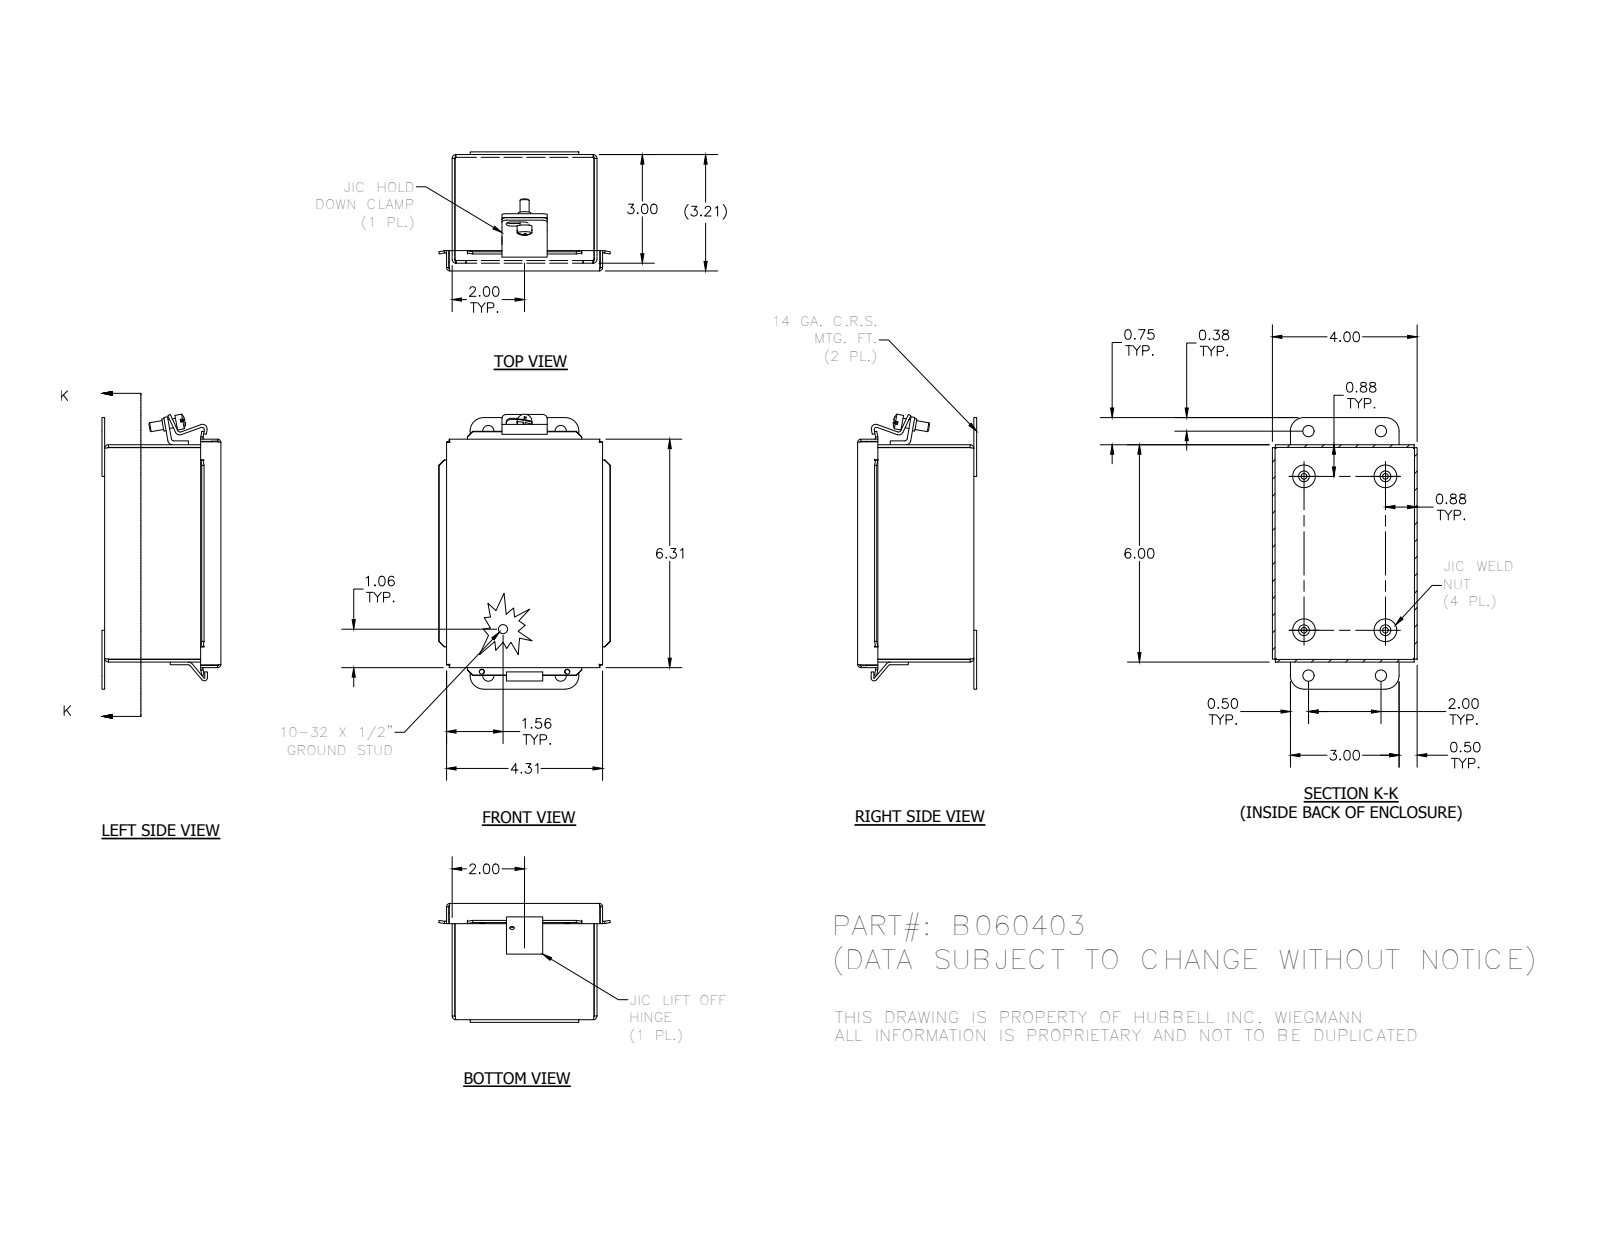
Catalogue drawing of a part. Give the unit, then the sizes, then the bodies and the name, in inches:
Units: inches
Overall size (bounding box): 7.593 × 4.739 × 3.287
Round holes (diameter × count): ⌀0.156 ×4, ⌀0.31 ×4, ⌀0.14 ×2, ⌀0.125 ×1, ⌀0.196 ×1
Round bosses / shafts (diameter × count): ⌀0.625 ×4, ⌀0.3 ×4, ⌀0.25 ×2, ⌀0.41 ×1, ⌀0.344 ×1, ⌀0.19 ×1
Partial cylindrical surfaces — rounded edges, fillets, slot ends (radius × count): R0.031 ×16, R0.093 ×8, R0.105 ×8, R0.125 ×4, R0.375 ×4, R0.063 ×3, R0.126 ×3, R0.133 ×2
Main face-to-face distances: 0.074, 3.926, 3.15, 3.212, 0.062, 3.076, 3.138, 5.926, 4, 3.852
Hole centre spacings: 1.256, 1.257, 2, 2.25, 2.465, 2.466, 4.25, 4.809
Volume: 12.28 in³ · Surface area: 323.2 in²
Bodies: 15 solids, 346 faces (227 planar, 77 cylindrical, 42 other)
Part name (STEP PRODUCT): B060403; 3499; 3481; C1001 (+7 more)
STEP written by: Autodesk Inventor 2012 (AUTOMOTIVE_DESIGN)
